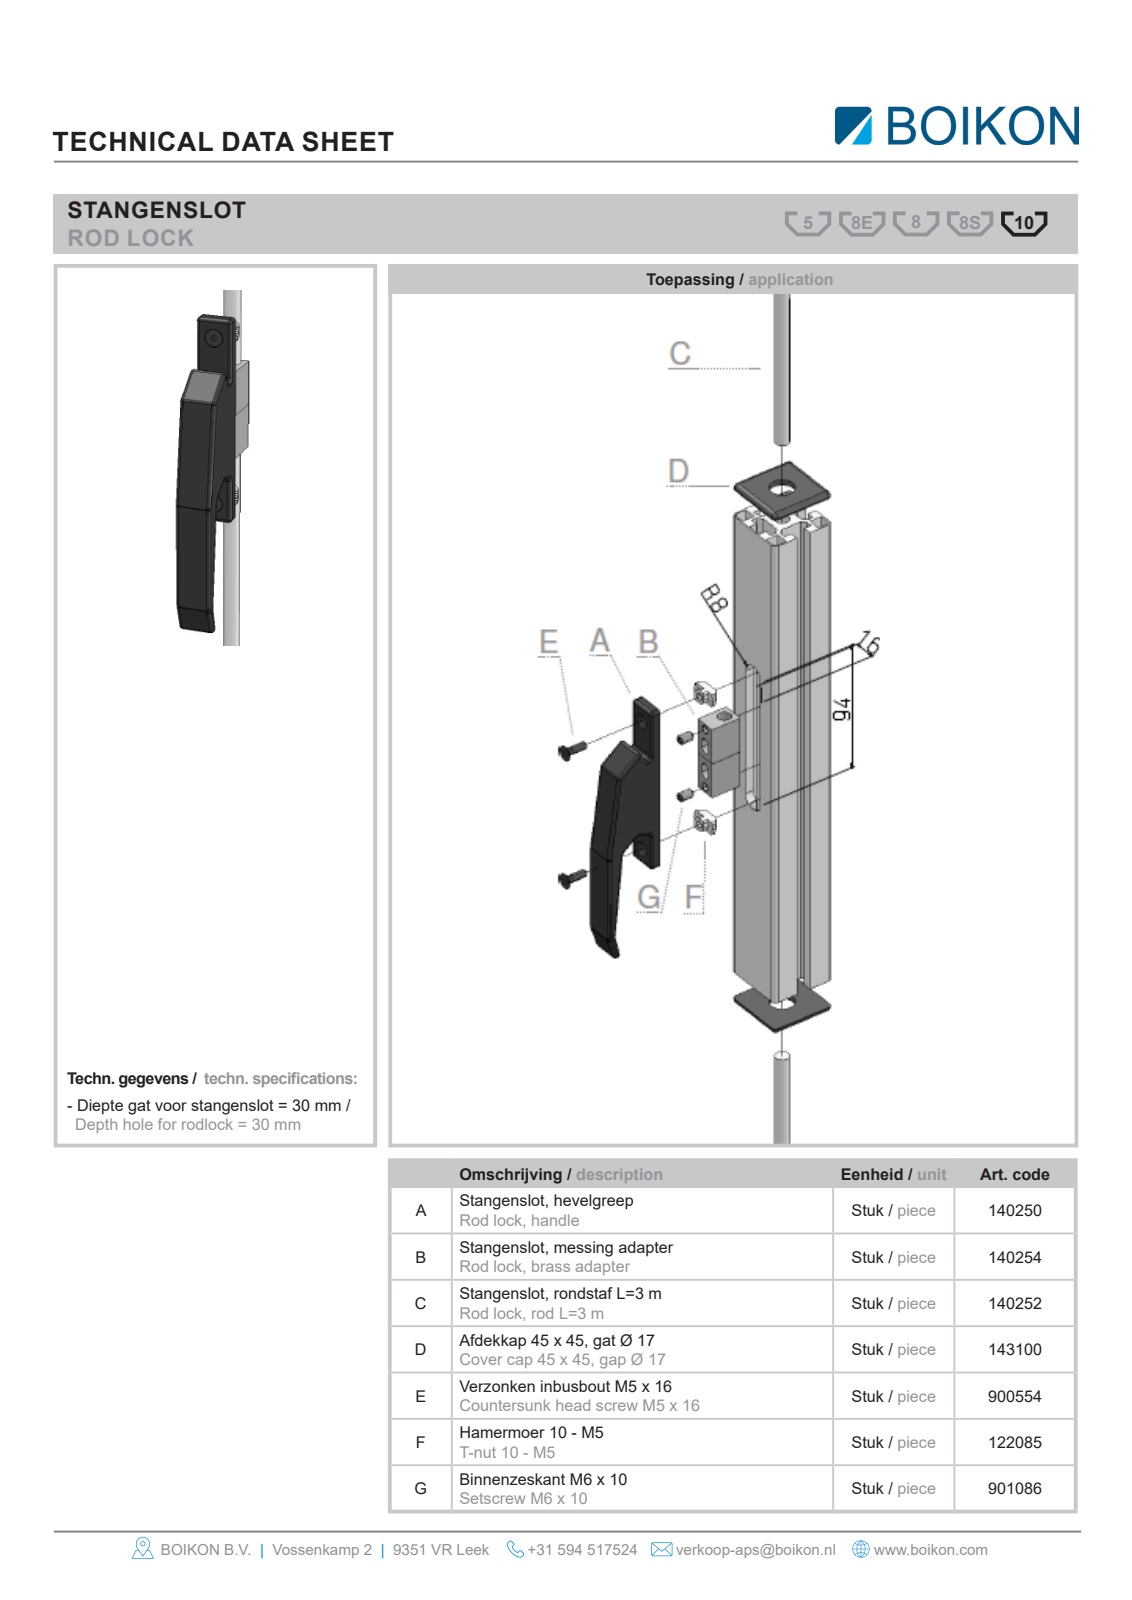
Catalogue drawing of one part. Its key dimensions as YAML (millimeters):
part_name: "Root; 140252RVS rondstaf rond 9.5 T-303 L=3mtrBOIKON0"
step_written_by: "HiCAD 2013 1802.4 Build 509 (AUTOMOTIVE_DESIGN)"
units: millimeters
bodies: {solids: 1, faces: 3, planar: 2, cylindrical: 1, other: 0}
overall_size: [3000, 9.5, 9.5]
volume: 212647
surface_area: 89677
round_bosses_or_shafts:
  - {diameter: 9.5, count: 1}
face_to_face_distances: [3000]
